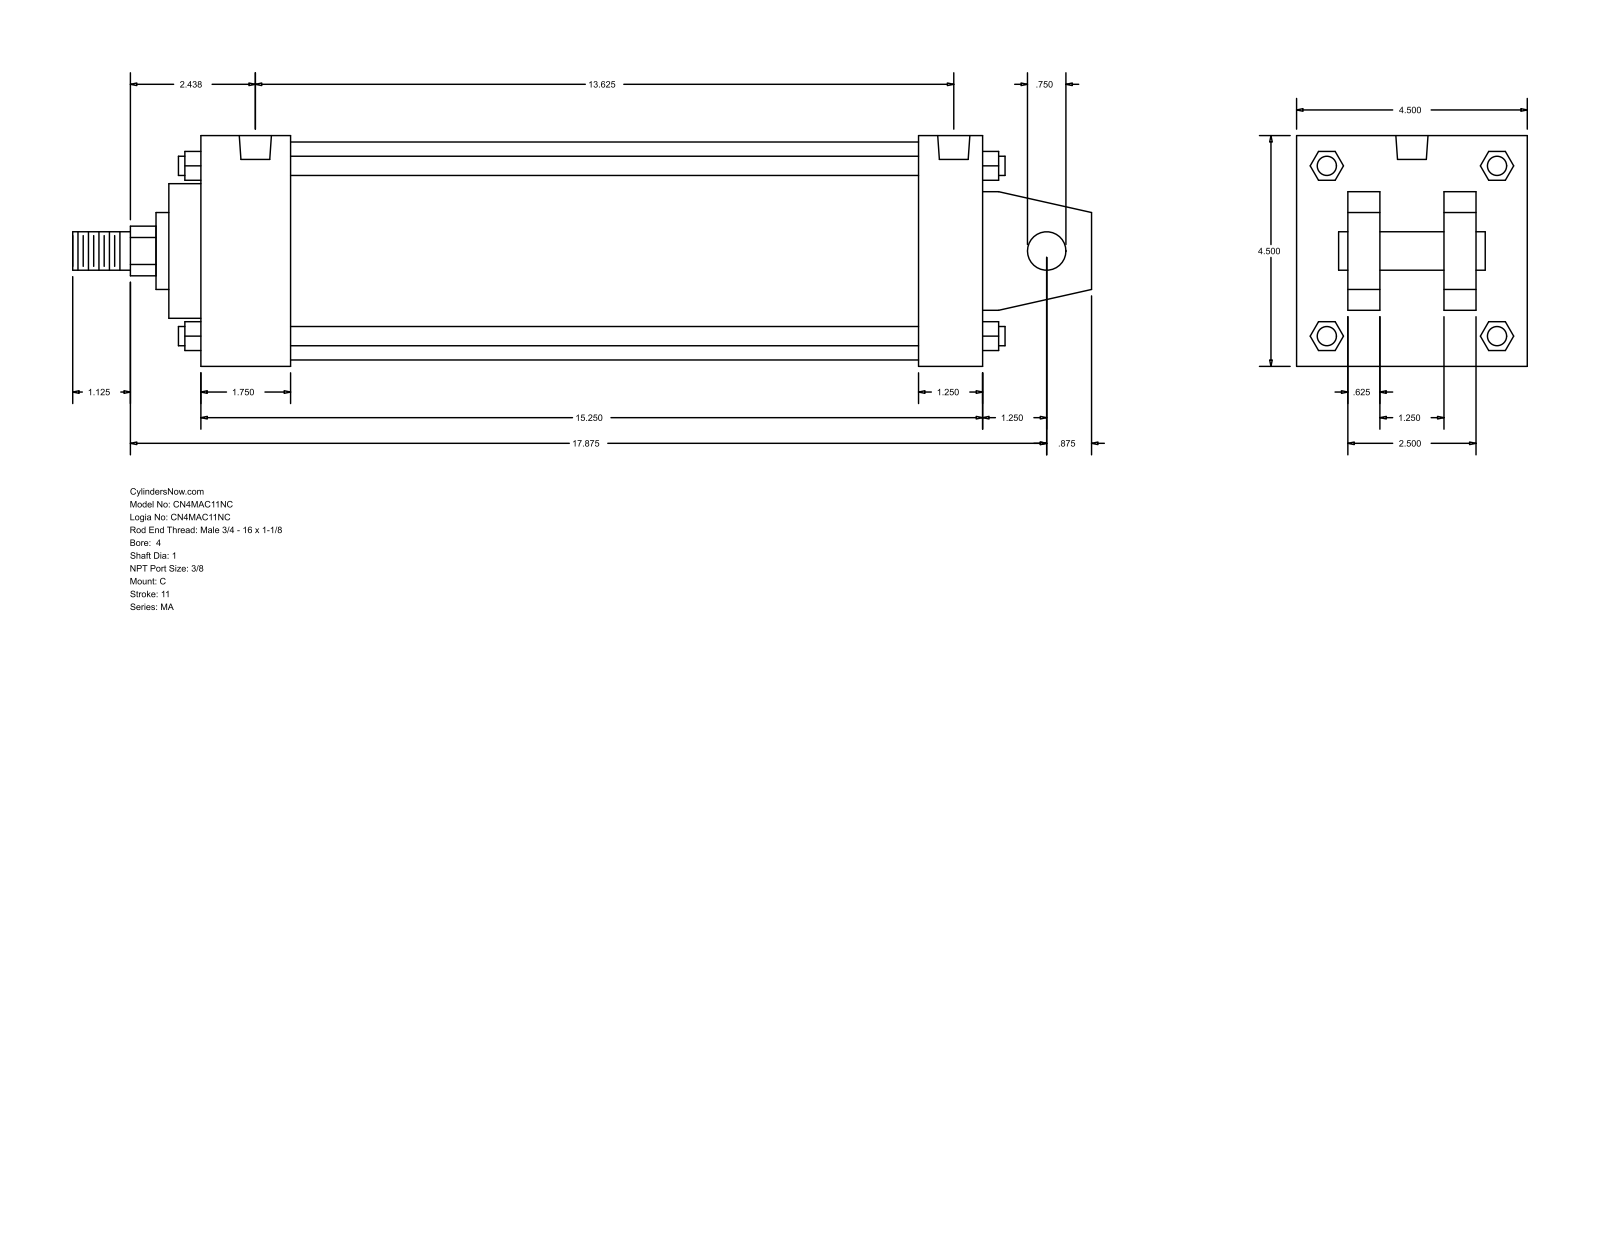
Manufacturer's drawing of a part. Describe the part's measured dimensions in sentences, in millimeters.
The part is named "MA_C__0400_1". Its 3-D file was written by "GSSL Pune (CONFIG_CONTROL_DESIGN)". It is 0 solids with 141 faces: 109 planar, 32 cylindrical and 0 other. Overall it measures 504.82 by 114.3 by 114.3 millimeters. Round holes: 4 of diameter 11.11, 2 of diameter 15.93. Round bosses or shafts: 4 of diameter 9.53, 2 of diameter 19.05, 1 of diameter 107.95, 1 of diameter 66.67, 1 of diameter 38.1, 1 of diameter 25.4. Partial cylindrical surfaces (rounded edges, fillets, slot ends): 1 of radius 12.29. The main face-to-face distances are 114.3, 387.35, 15.87, 73.03, 41.27, 25.4, 88.9, 47.63, 355.6, 31.75. The hole center spacings are 4.76, 336.56, 341.32, 346.08.
